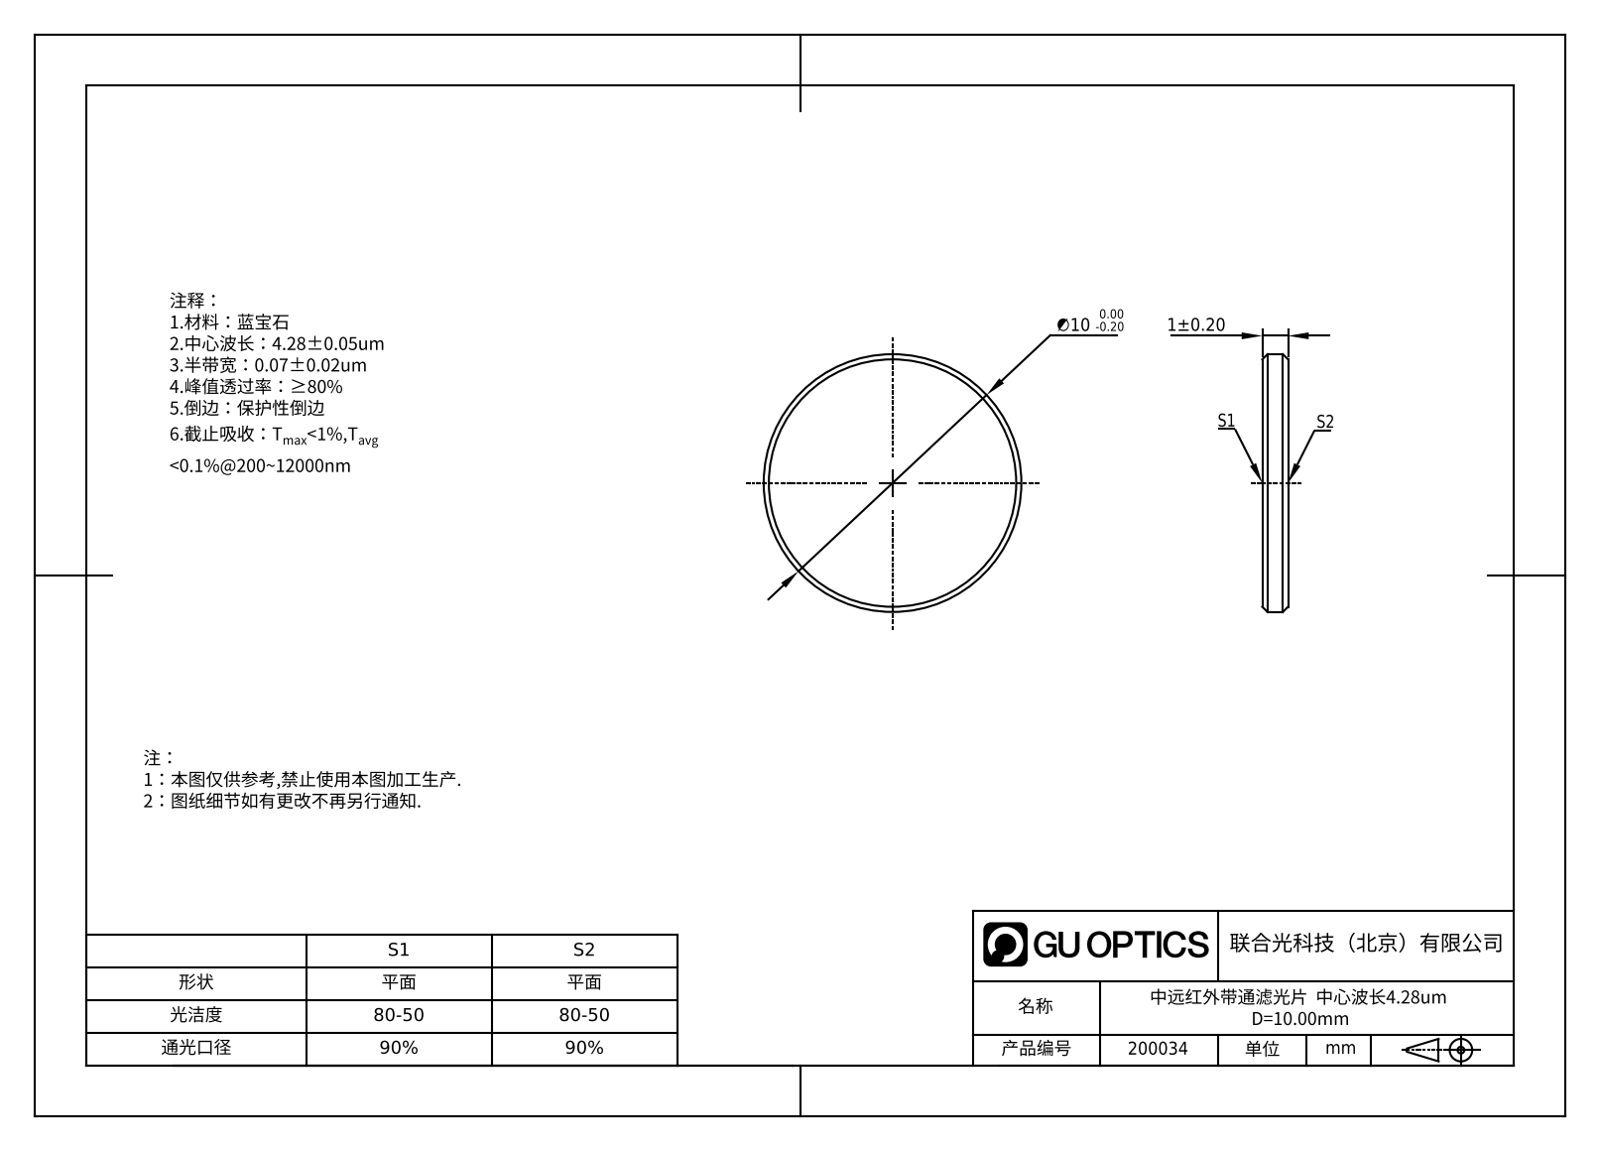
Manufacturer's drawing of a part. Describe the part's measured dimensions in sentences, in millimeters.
The part is named "GNIF-070-4280-D10". Its 3-D file was written by "SolidWorks 2022 (AUTOMOTIVE_DESIGN)". It is 1 solid with 8 faces: 2 planar, 2 cylindrical and 4 other. Overall it measures 10 by 10 by 1 millimeters. Its volume is 77 cubic millimeters and its surface area 181 square millimeters. Round bosses or shafts: 1 of diameter 10. The main face-to-face distances are 1.
